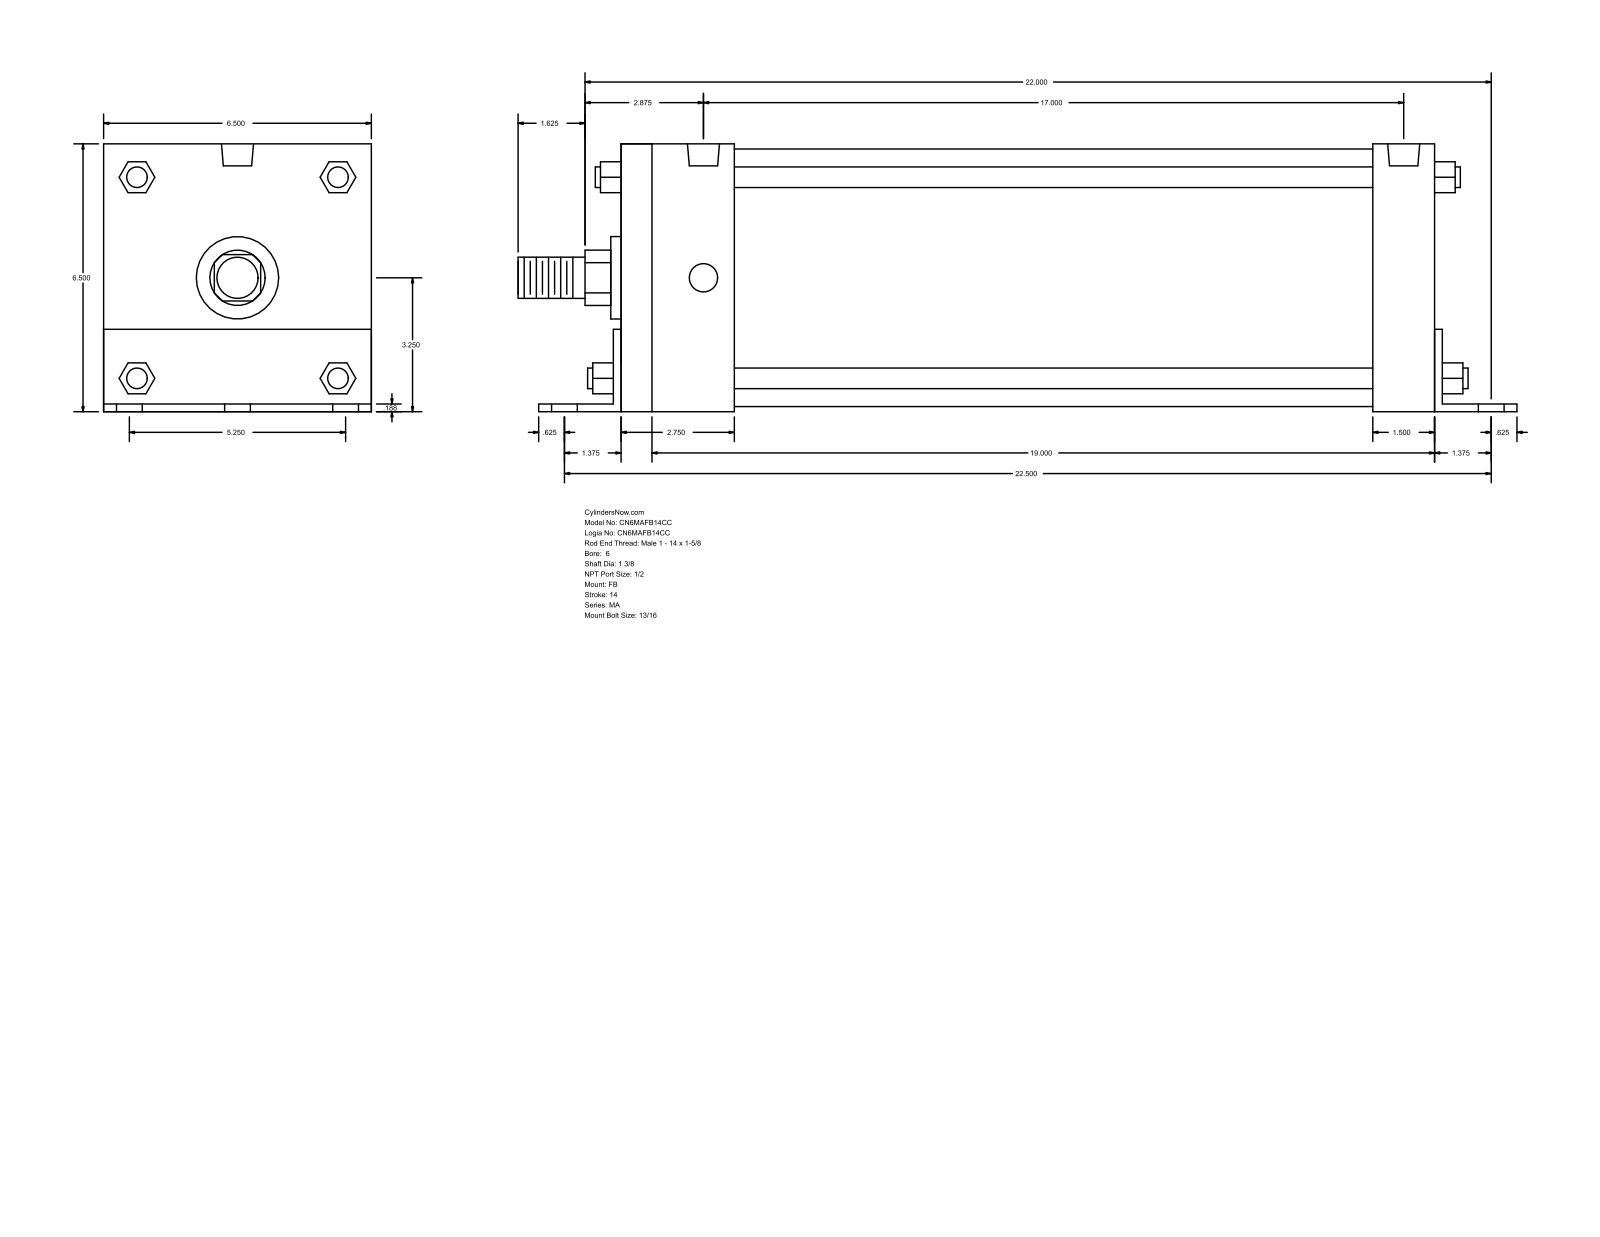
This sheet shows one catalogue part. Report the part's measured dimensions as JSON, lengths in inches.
{"part_name": "MA_FB__0600_1.375", "step_written_by": "GSSL Pune (CONFIG_CONTROL_DESIGN)", "units": "inches", "bodies": {"solids": 0, "faces": 140, "planar": 105, "cylindrical": 35, "other": 0}, "overall_size": [24.125, 6.502, 6.5], "round_holes": [[0.813, 6], [0.687, 4], [0.778, 2]], "round_bosses_or_shafts": [[0.5, 4], [6.25, 1], [2, 1], [1.375, 1], [1, 1]], "partial_cylinders_radius": [[0.672, 1], [1.262, 1]], "face_to_face_distances": [6.5, 0.187, 19.625, 6.502, 0.185, 6.315, 0.188, 1.5, 1.687, 20], "hole_center_spacings": [2.625, 22.528, 22.375, 3.3, 3.377, 4.276, 5.25, 16.875]}
